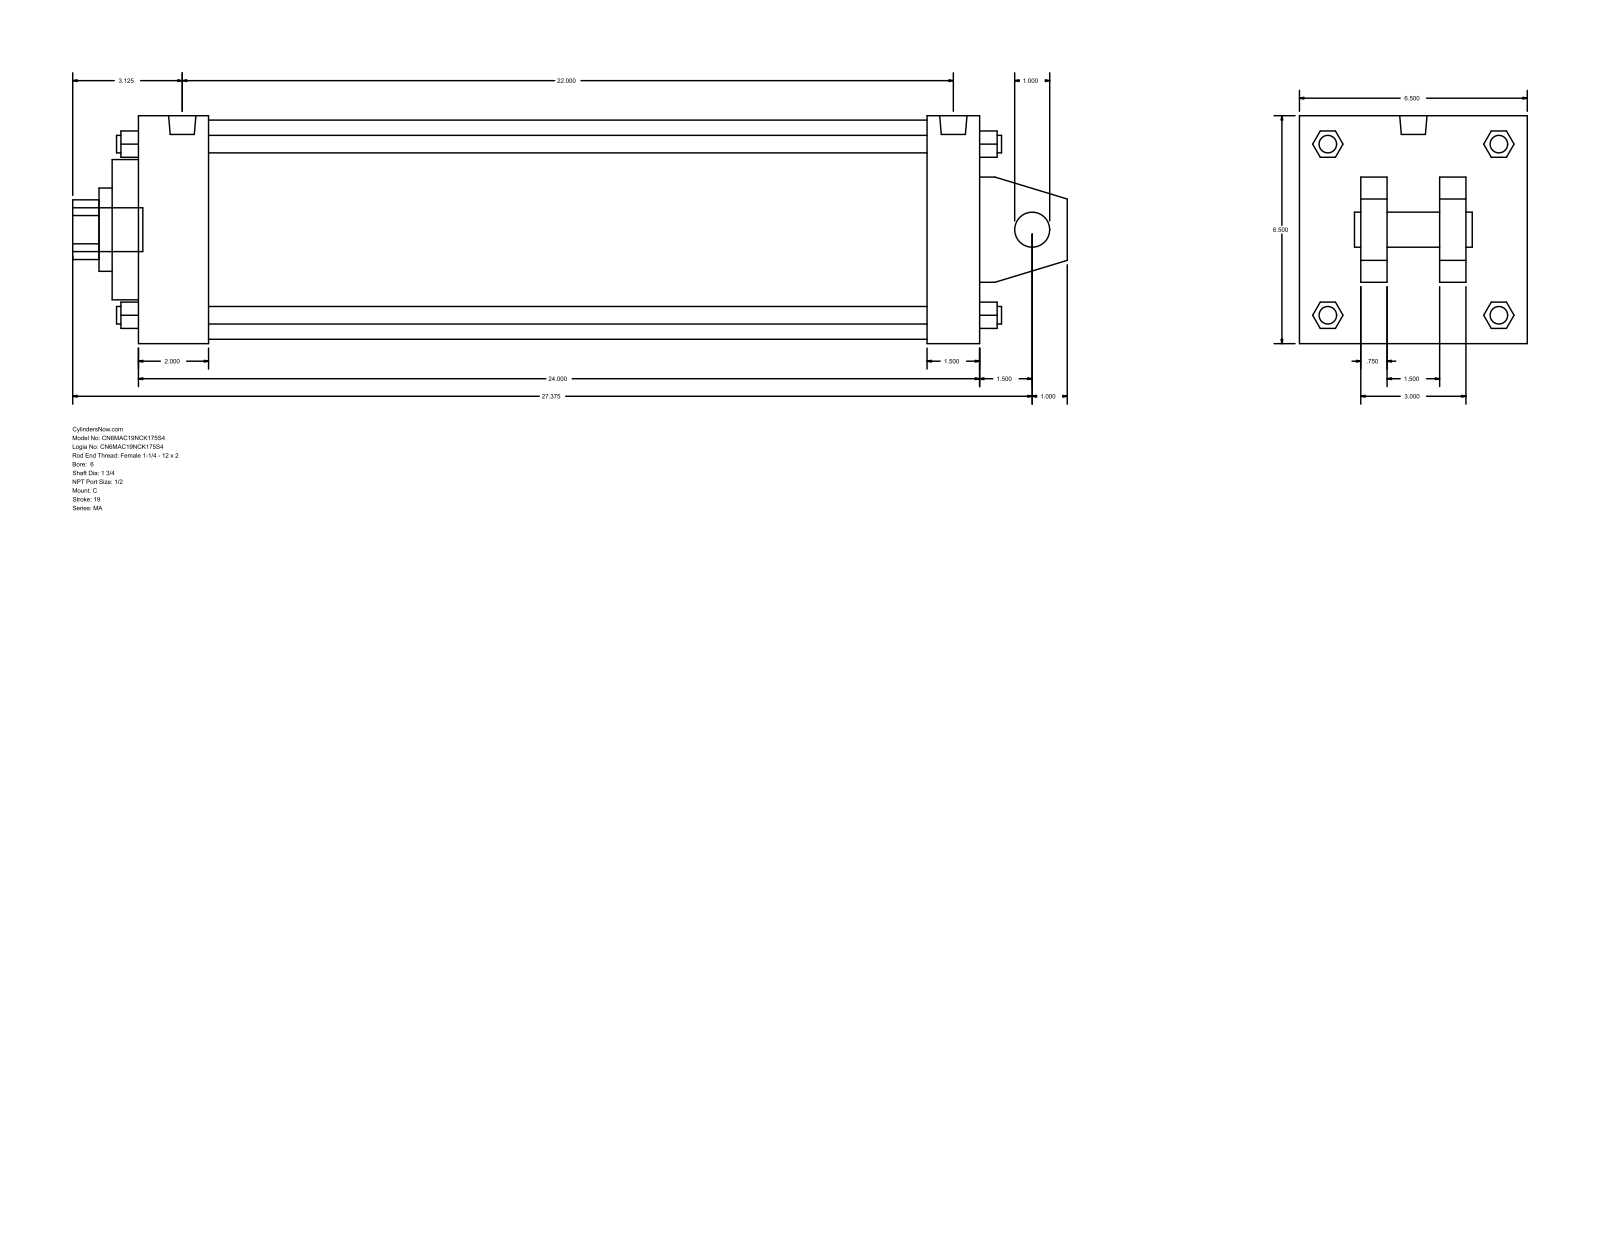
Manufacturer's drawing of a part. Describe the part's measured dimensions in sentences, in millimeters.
The part is named "MA_C__0600_1.75". Its 3-D file was written by "GSSL Pune (CONFIG_CONTROL_DESIGN)". It is 0 solids with 141 faces: 109 planar, 32 cylindrical and 0 other. Overall it measures 720.73 by 165.1 by 165.1 millimeters. Round holes: 1 of diameter 25.4, 1 of diameter 44.45, 1 of diameter 60.33, 1 of diameter 101.6, 1 of diameter 158.75. Round bosses or shafts: 4 of diameter 17.46, 4 of diameter 12.7, 2 of diameter 19.77, 1 of diameter 31.75. Partial cylindrical surfaces (rounded edges, fillets, slot ends): 1 of radius 21.63. The main face-to-face distances are 165.1, 609.61, 19.05, 63.5, 101.6, 50.8, 44.45, 120.65, 571.5, 57.15.
